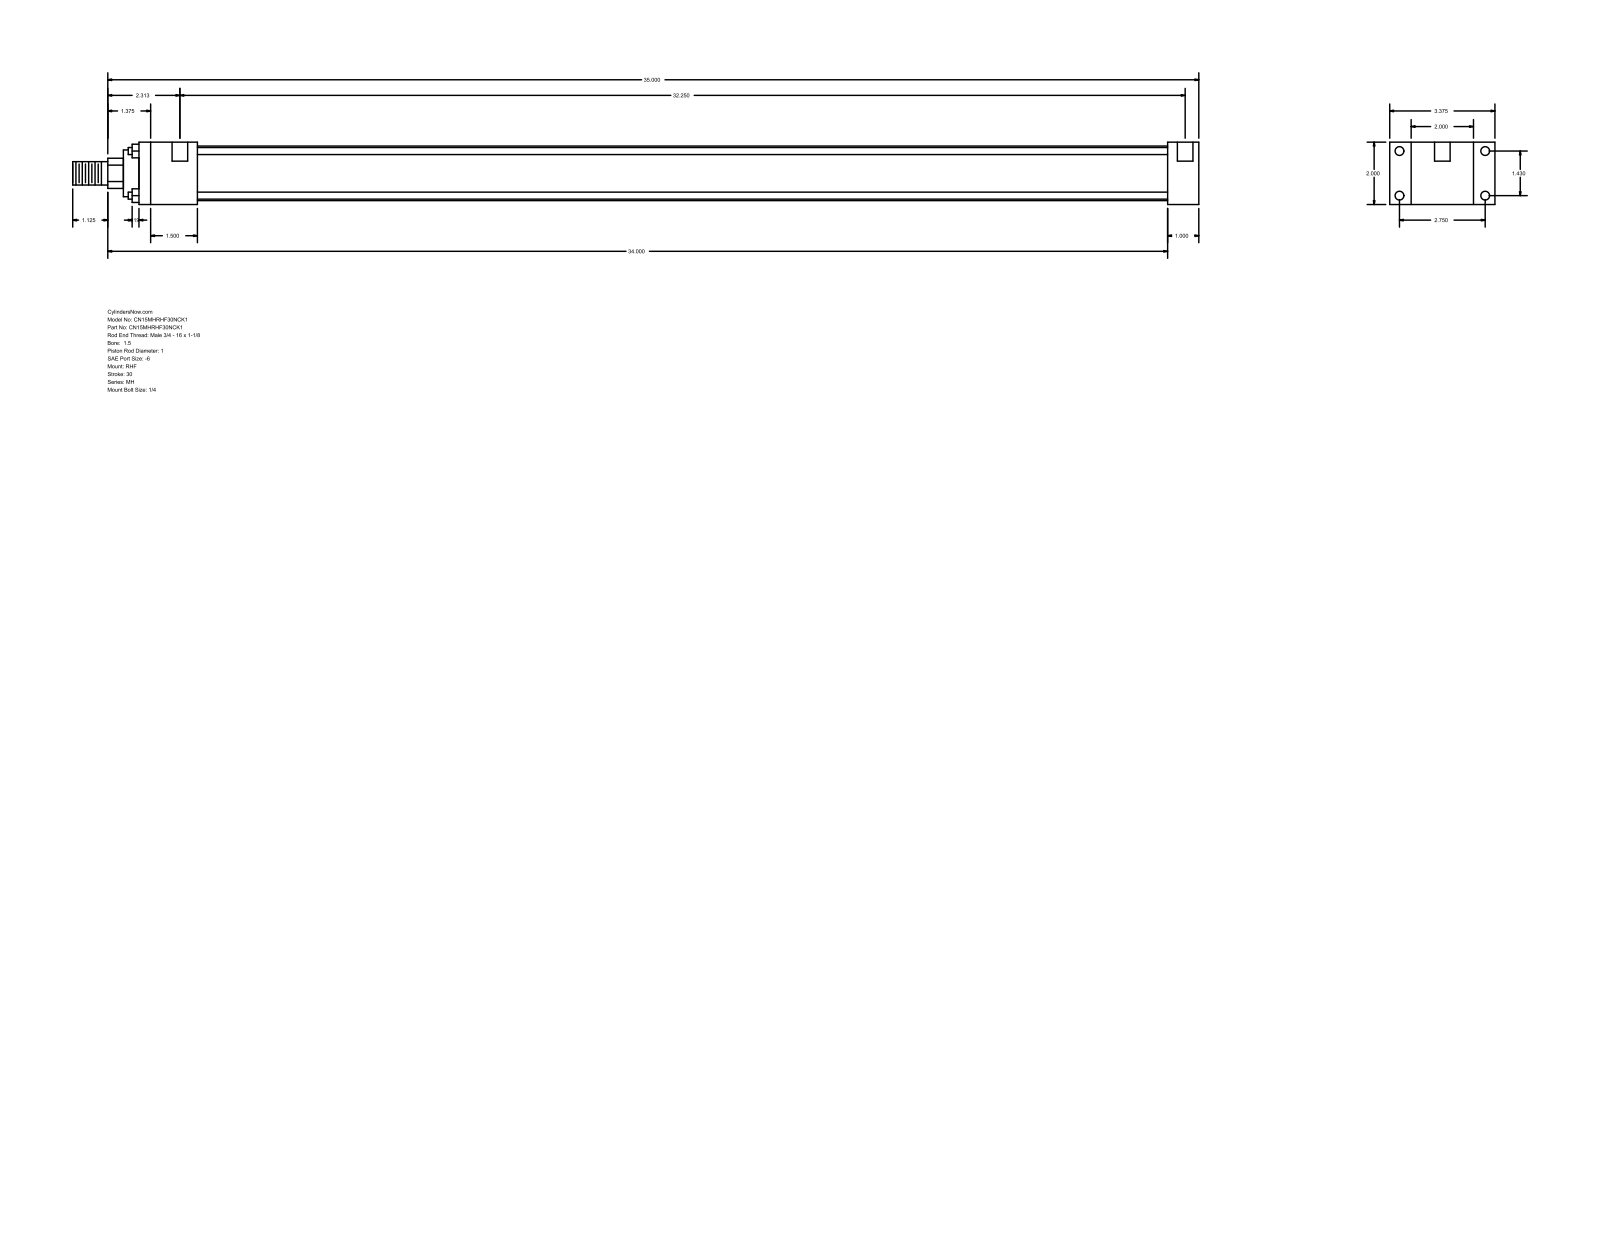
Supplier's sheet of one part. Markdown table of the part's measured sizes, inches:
| quantity | value |
| --- | --- |
| part name | MH_RHF__0150_1 |
| STEP written by | GSSL Pune (CONFIG_CONTROL_DESIGN) |
| units | inches |
| bodies | 0 solids, 88 faces (60 planar, 28 cylindrical, 0 other) |
| overall size | 36.125 × 3.375 × 2 |
| round holes (diameter × count) | 0.219 × 4, 0.281 × 4, 0.5 × 2 |
| round bosses / shafts (diameter × count) | 0.225 × 4, 1.75 × 1, 1.5 × 1, 1 × 1, 0.75 × 1 |
| partial cylindrical surfaces (radius × count) | 0.484 × 1 |
| main face-to-face distances | 2, 1, 0.687, 2.687, 3.375, 34, 33, 1.875, 31.125, 32.125 |
| hole center spacings | 1.43, 2.75, 3.099, 32.375, 0.125, 32.25 |
